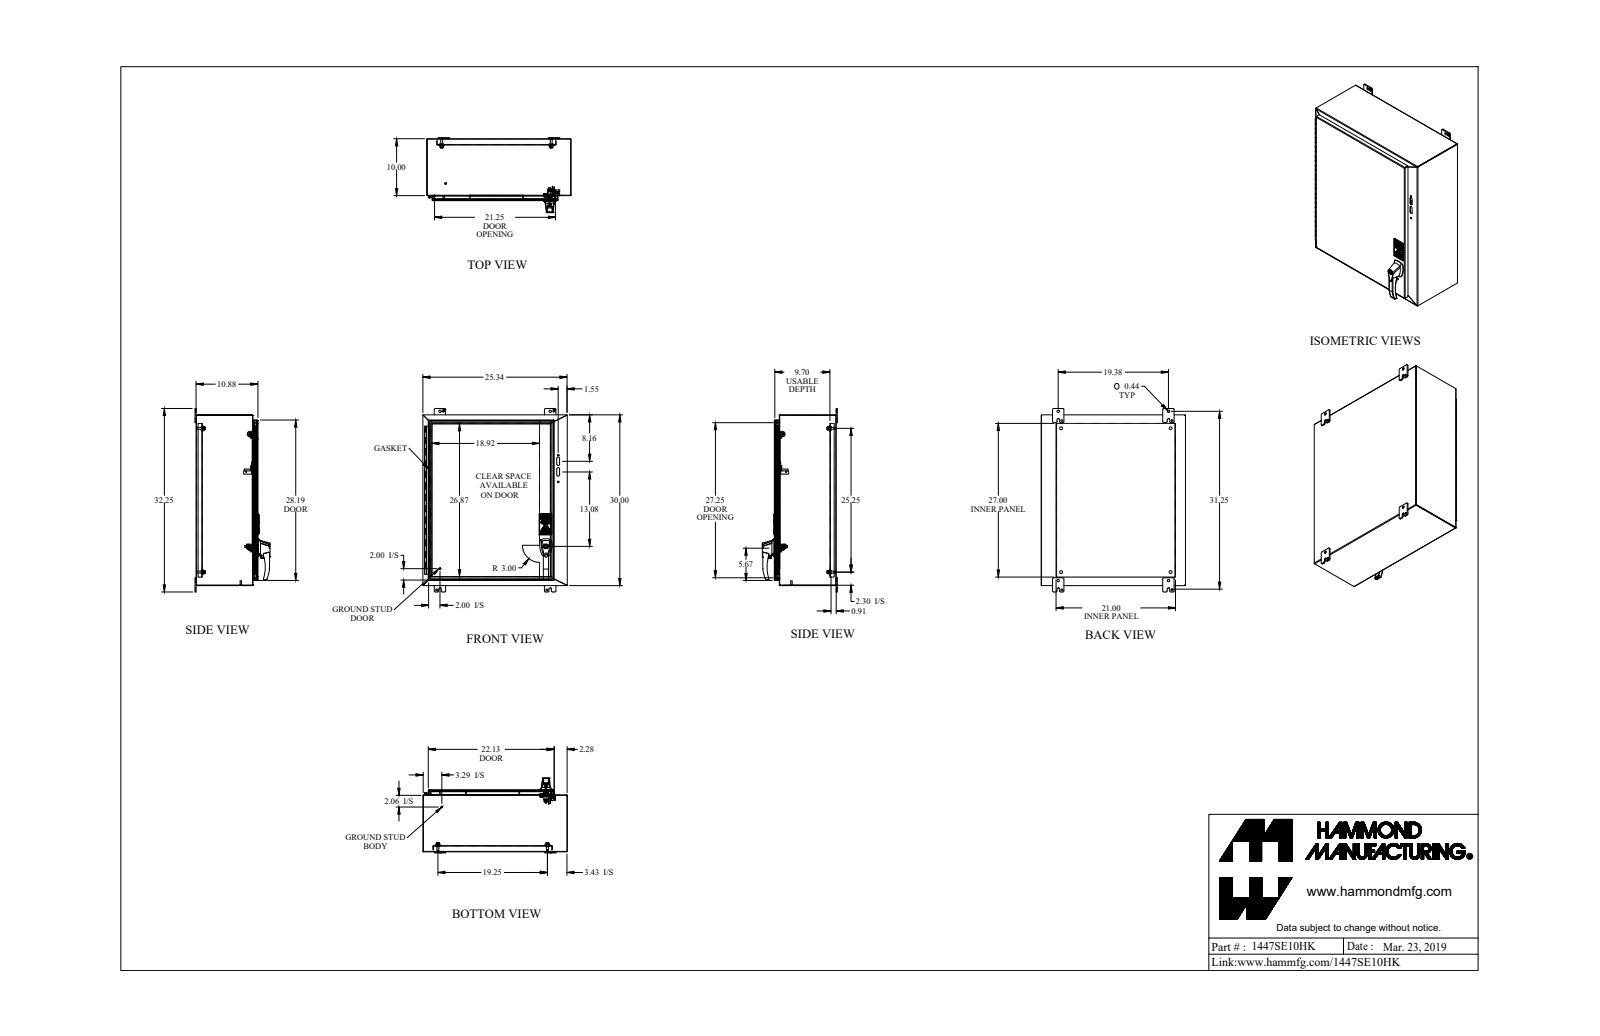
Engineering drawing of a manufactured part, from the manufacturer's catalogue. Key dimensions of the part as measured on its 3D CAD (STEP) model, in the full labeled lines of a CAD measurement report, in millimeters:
Part name (STEP PRODUCT): 1447SE10HK
STEP written by: SolidWorks 2019 (AUTOMOTIVE_DESIGN)
Units: millimetres
Bodies: 49 solids, 1191 faces (735 planar, 341 cylindrical, 115 other)
Overall size (bounding box): 819.2 × 644.5 × 334.7
Volume: 4 785 000 mm³ · Surface area: 4 754 000 mm²
Round holes (diameter × count): ⌀8 ×5, ⌀4.5 ×4, ⌀11.1 ×4, ⌀12.7 ×4, ⌀4 ×2, ⌀4.4 ×2, ⌀5.5 ×2, ⌀6.4 ×2, ⌀7.1 ×2, ⌀7.8 ×2, ⌀10.5 ×2, ⌀11.3 ×2
Round bosses / shafts (diameter × count): ⌀9.5 ×8, ⌀6.4 ×7, ⌀25.4 ×4, ⌀16.5 ×4, ⌀8.4 ×4, ⌀12.7 ×2, ⌀10.2 ×2, ⌀7.1 ×2
Partial cylindrical surfaces — rounded edges, fillets, slot ends (radius × count): R2 ×28, R4.8 ×24, R0.2 ×16, R6.4 ×12, R3.2 ×11, R0.8 ×8, R3.8 ×8, R5.5 ×8
Main face-to-face distances: 1.8, 274.4, 272.6, 276.2, 2.4, 642.7, 248.2, 246.4, 26.2, 28
Hole centre spacings: 492.1, 28.2, 489, 44.1, 44.1, 47.1, 478.4, 485.4
